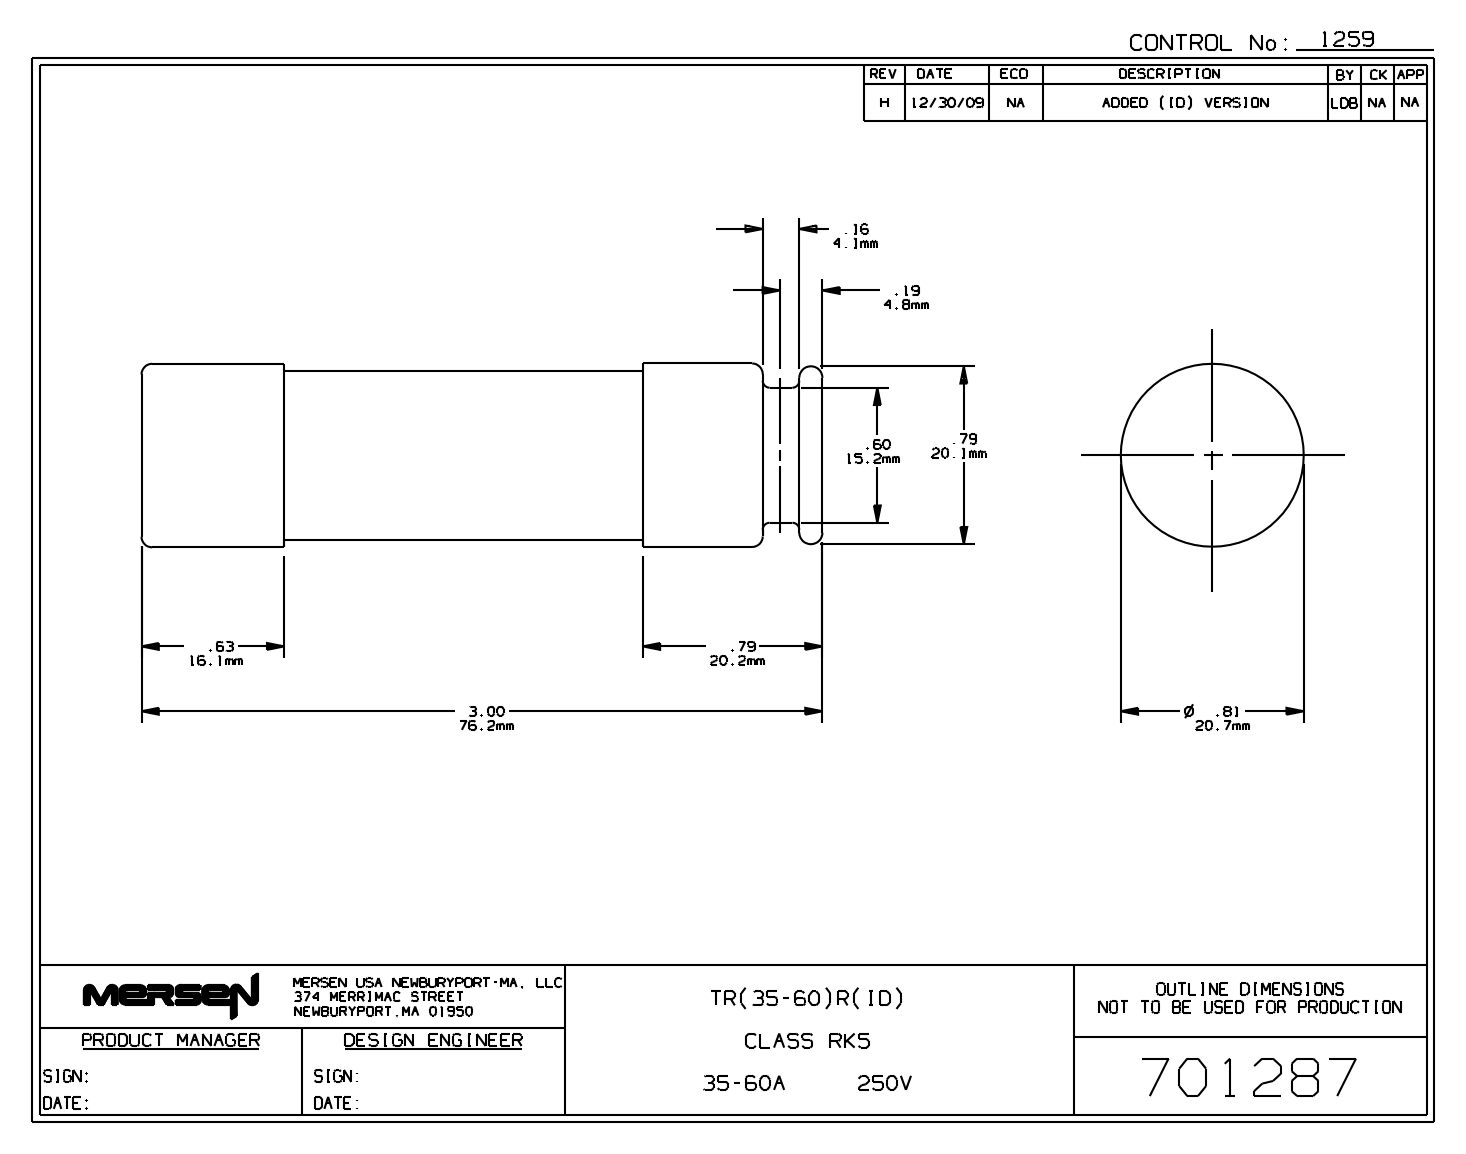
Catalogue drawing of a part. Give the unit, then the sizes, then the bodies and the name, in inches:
Units: inches
Overall size (bounding box): 3 × 0.836 × 0.836
Round holes (diameter × count): ⌀0.156 ×4, ⌀0.322 ×1, ⌀0.382 ×1, ⌀0.566 ×1, ⌀0.625 ×1, ⌀0.755 ×1, ⌀0.782 ×1
Round bosses / shafts (diameter × count): ⌀0.816 ×1, ⌀0.767 ×1, ⌀0.744 ×1, ⌀0.6 ×1, ⌀0.5 ×1, ⌀0.438 ×1, ⌀0.365 ×1, ⌀0.311 ×1
Partial cylindrical surfaces — rounded edges, fillets, slot ends (radius × count): R0.01 ×8, R0.027 ×8
Main face-to-face distances: 0.017, 2.983, 0.017, 0.022, 3, 2.966, 0.265, 0.04, 0.057, 0.028
Hole centre spacings: 0.437, 1.203, 1.64
Volume: 0.505 in³ · Surface area: 29.69 in²
Bodies: 13 solids, 247 faces (105 planar, 70 cylindrical, 72 other)
Part name (STEP PRODUCT): 701287
STEP written by: SolidWorks 2016 (AUTOMOTIVE_DESIGN)
